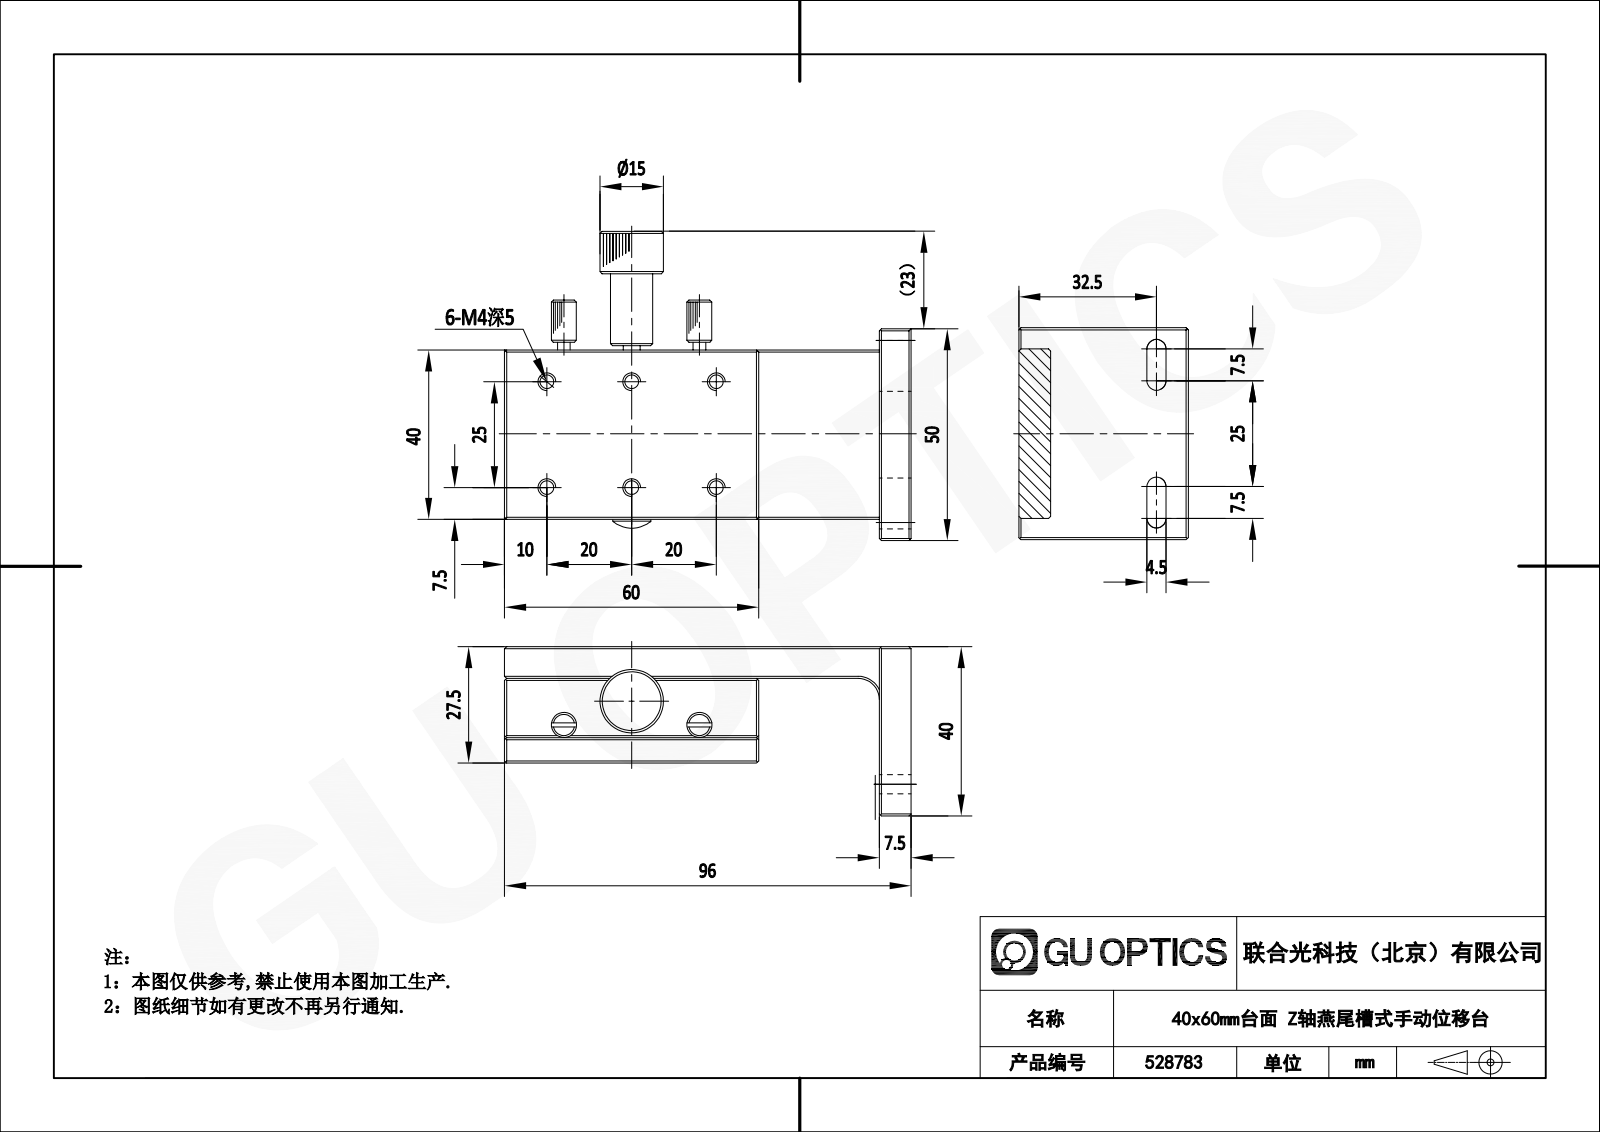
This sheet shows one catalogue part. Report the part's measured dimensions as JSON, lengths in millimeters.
{"part_name": "528783", "step_written_by": "SolidWorks 2020 (CONFIG_CONTROL_DESIGN)", "units": "millimeters", "bodies": {"solids": 13, "faces": 726, "planar": 383, "cylindrical": 176, "other": 167}, "overall_size": [96, 77.9, 40], "volume_mm3": 89074, "surface_area_mm2": 41147, "round_holes": [[2.5, 13], [3.3, 10], [4.5, 7], [8, 7], [3.4, 3], [6, 3], [2.05, 2], [2.8, 2], [4, 1], [4.1, 1]], "round_bosses_or_shafts": [[10, 2], [9, 2], [7, 2], [2.95, 2], [8, 1], [7.4, 1], [6.85, 1], [3, 1]], "partial_cylinders_radius": [[2.25, 4], [2, 2], [10, 1]], "face_to_face_distances": [7.5, 20, 6, 14, 27.5, 21.5, 40, 10, 3.8, 1], "hole_center_spacings": [15.21, 31.32, 5.59, 14.33, 14.58, 17.68, 19.21, 20]}
